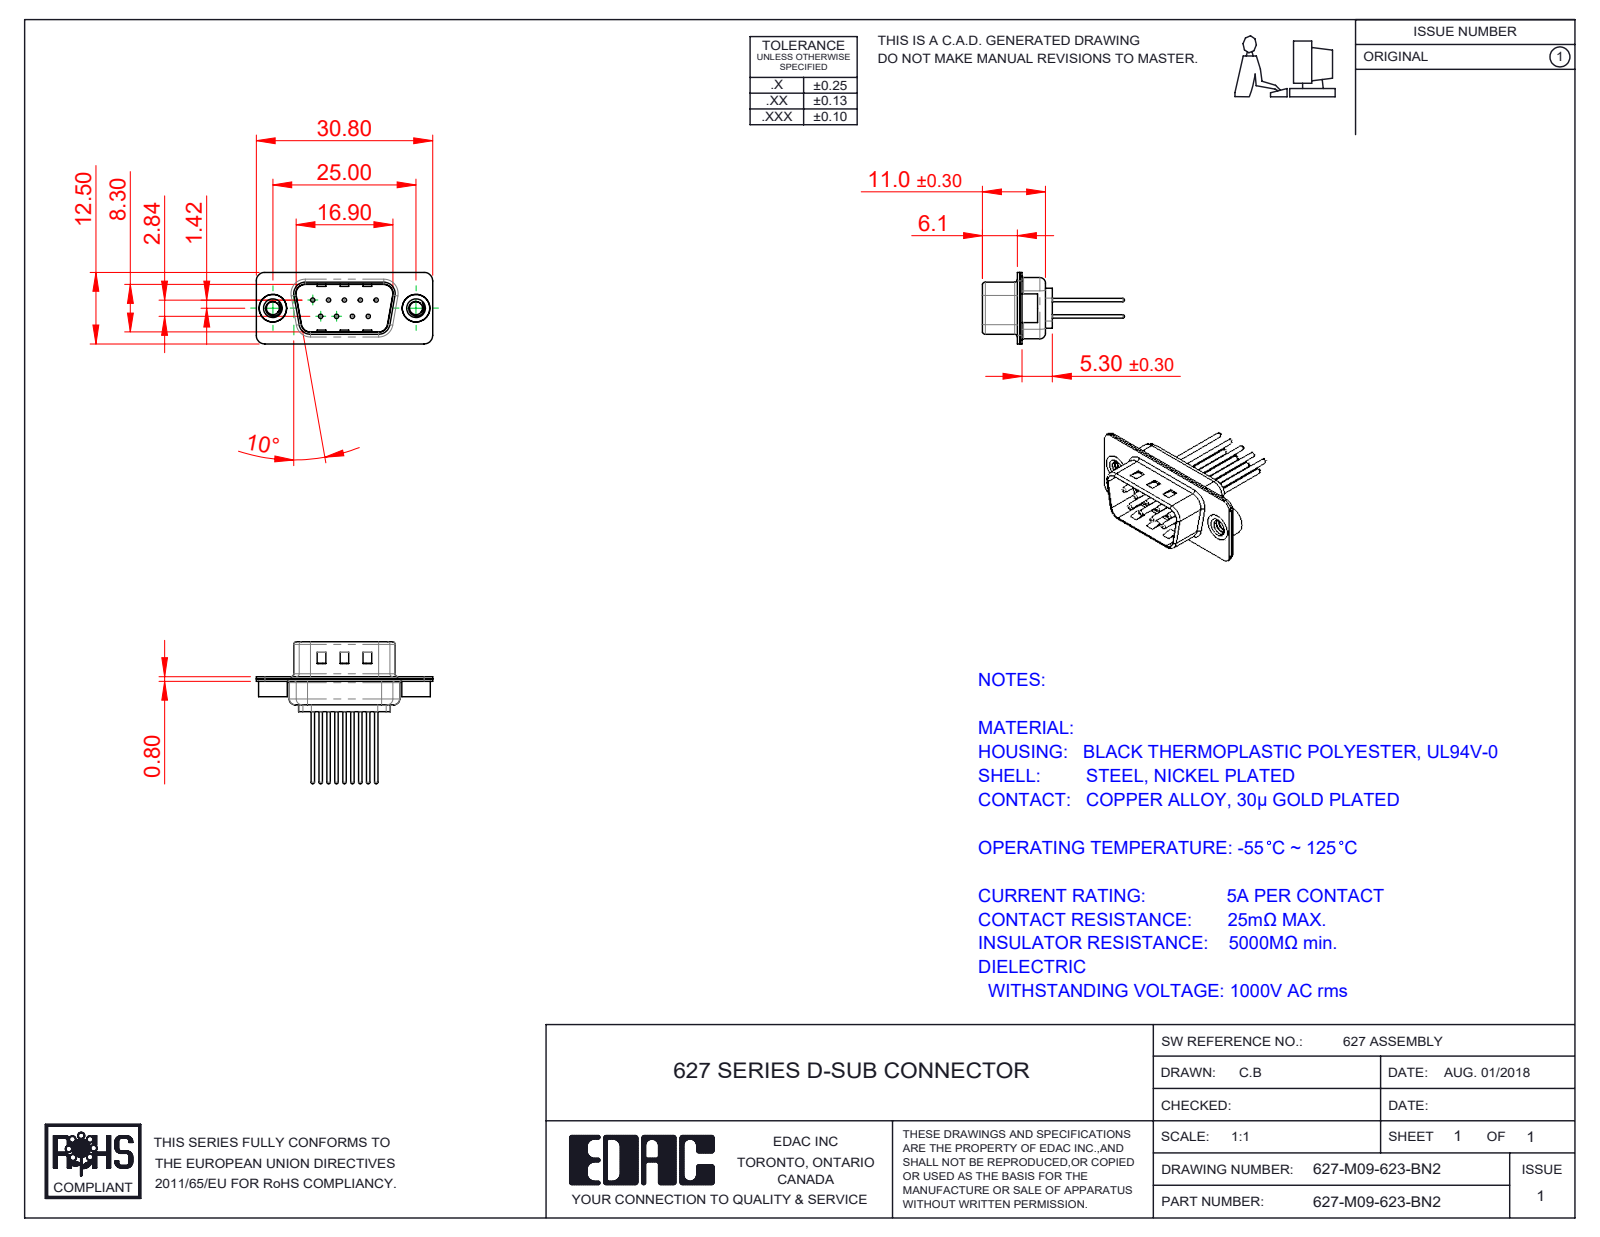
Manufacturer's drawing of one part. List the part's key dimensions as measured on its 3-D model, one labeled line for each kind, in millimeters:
Part name (STEP PRODUCT): 627M Contact Row 1_23; 627M Shell Front_09 Contacts; 627M 4-40 Threaded Rivet; 627M Shell Rear_09 Contacts (+3 more)
STEP written by: SolidWorks 2020 (CONFIG_CONTROL_DESIGN)
Units: millimetres
Bodies: 14 solids, 637 faces (170 planar, 255 cylindrical, 212 other)
Overall size (bounding box): 30.8 × 24.77 × 12.5
Volume: 1 328 mm³ · Surface area: 3 691 mm²
Round holes (diameter × count): ⌀0.75 ×9, ⌀1.6 ×9, ⌀2 ×9, ⌀2.26 ×2, ⌀4 ×2, ⌀4.8 ×2
Round bosses / shafts (diameter × count): ⌀1.5 ×9, ⌀0.6 ×9, ⌀5 ×2, ⌀4.9 ×2
Partial cylindrical surfaces — rounded edges, fillets, slot ends (radius × count): R1.5 ×16, R2 ×12, R0.5 ×8, R1.6 ×8, R0.25 ×4, R0.6 ×4, R0.65 ×4, R0.9 ×4
Main face-to-face distances: 0.4, 0.8, 9.5, 9.1, 8.7, 0.65, 9.9, 1.2, 6.1, 5.3
Hole centre spacings: 3.16, 2.77, 5.54, 5.03, 5.04, 8.31, 7.1, 7.48
